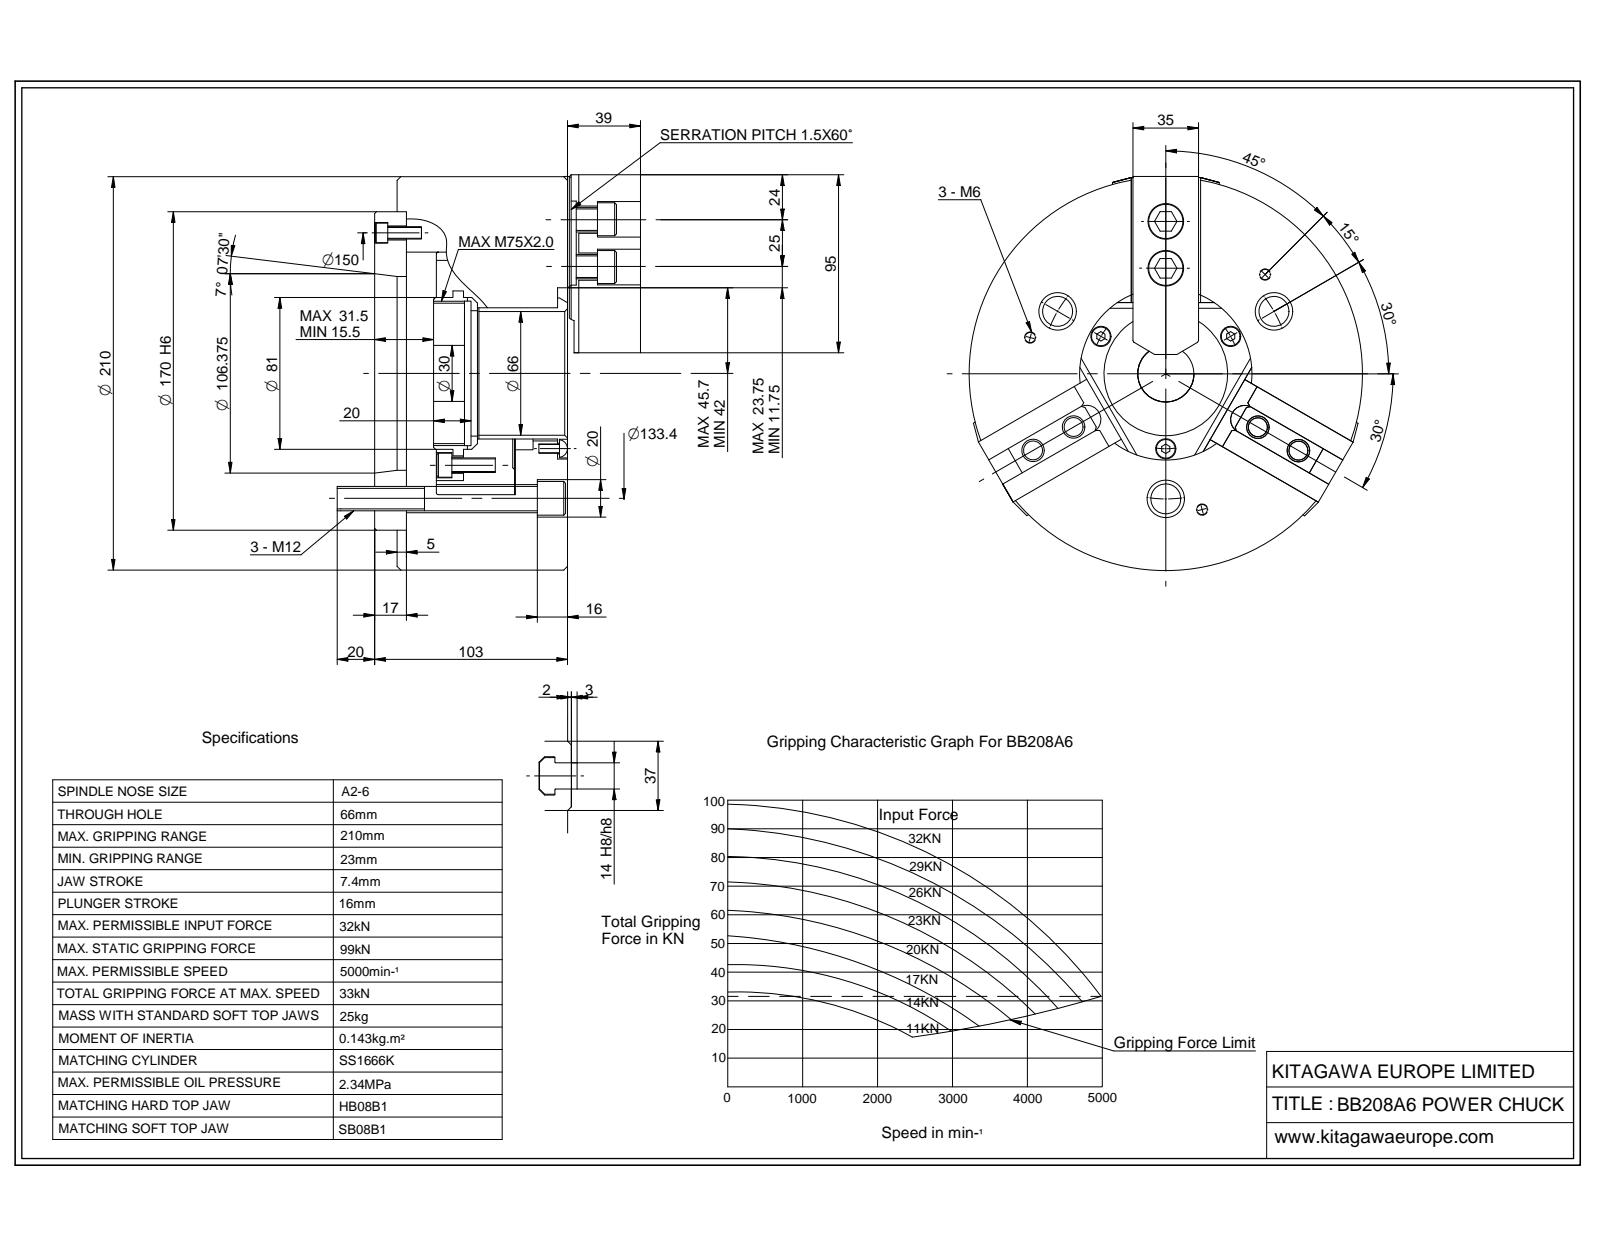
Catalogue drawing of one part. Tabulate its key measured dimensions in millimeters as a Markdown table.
| quantity | value |
| --- | --- |
| part name | BB208A615 |
| STEP written by | ST-DEVELOPER v16.7 (AUTOMOTIVE_DESIGN) |
| units | millimeters |
| bodies | 1 solid, 2530 faces (1780 planar, 335 cylindrical, 415 other) |
| overall size | 211.21 × 210 × 149.5 |
| volume | 2 767 000 mm³ |
| surface area | 338 857 mm² |
| round holes (diameter × count) | 3.8 × 12, 12 × 9, 4.92 × 8, 13.5 × 8, 6 × 7, 8 × 6, 9 × 6, 14 × 6, 6.65 × 5, 11 × 5, 5 × 4, 10 × 4 |
| round bosses / shafts (diameter × count) | 18 × 6, 13 × 5, 18.2 × 3, 12 × 3, 9.5 × 3, 5 × 3, 210 × 1, 118.7 × 1 |
| partial cylindrical surfaces (radius × count) | 2 × 18, 5 × 12, 0.4 × 6, 1 × 6, 1.2 × 6, 6 × 6, 6.5 × 6, 7 × 6 |
| main face-to-face distances | 12, 16.5, 91, 103, 20, 32, 15, 54.5, 16, 10.5 |
| hole center spacings | 66.67, 116.68, 51, 76.84, 88.33, 102.09, 124.25, 139.71 |
